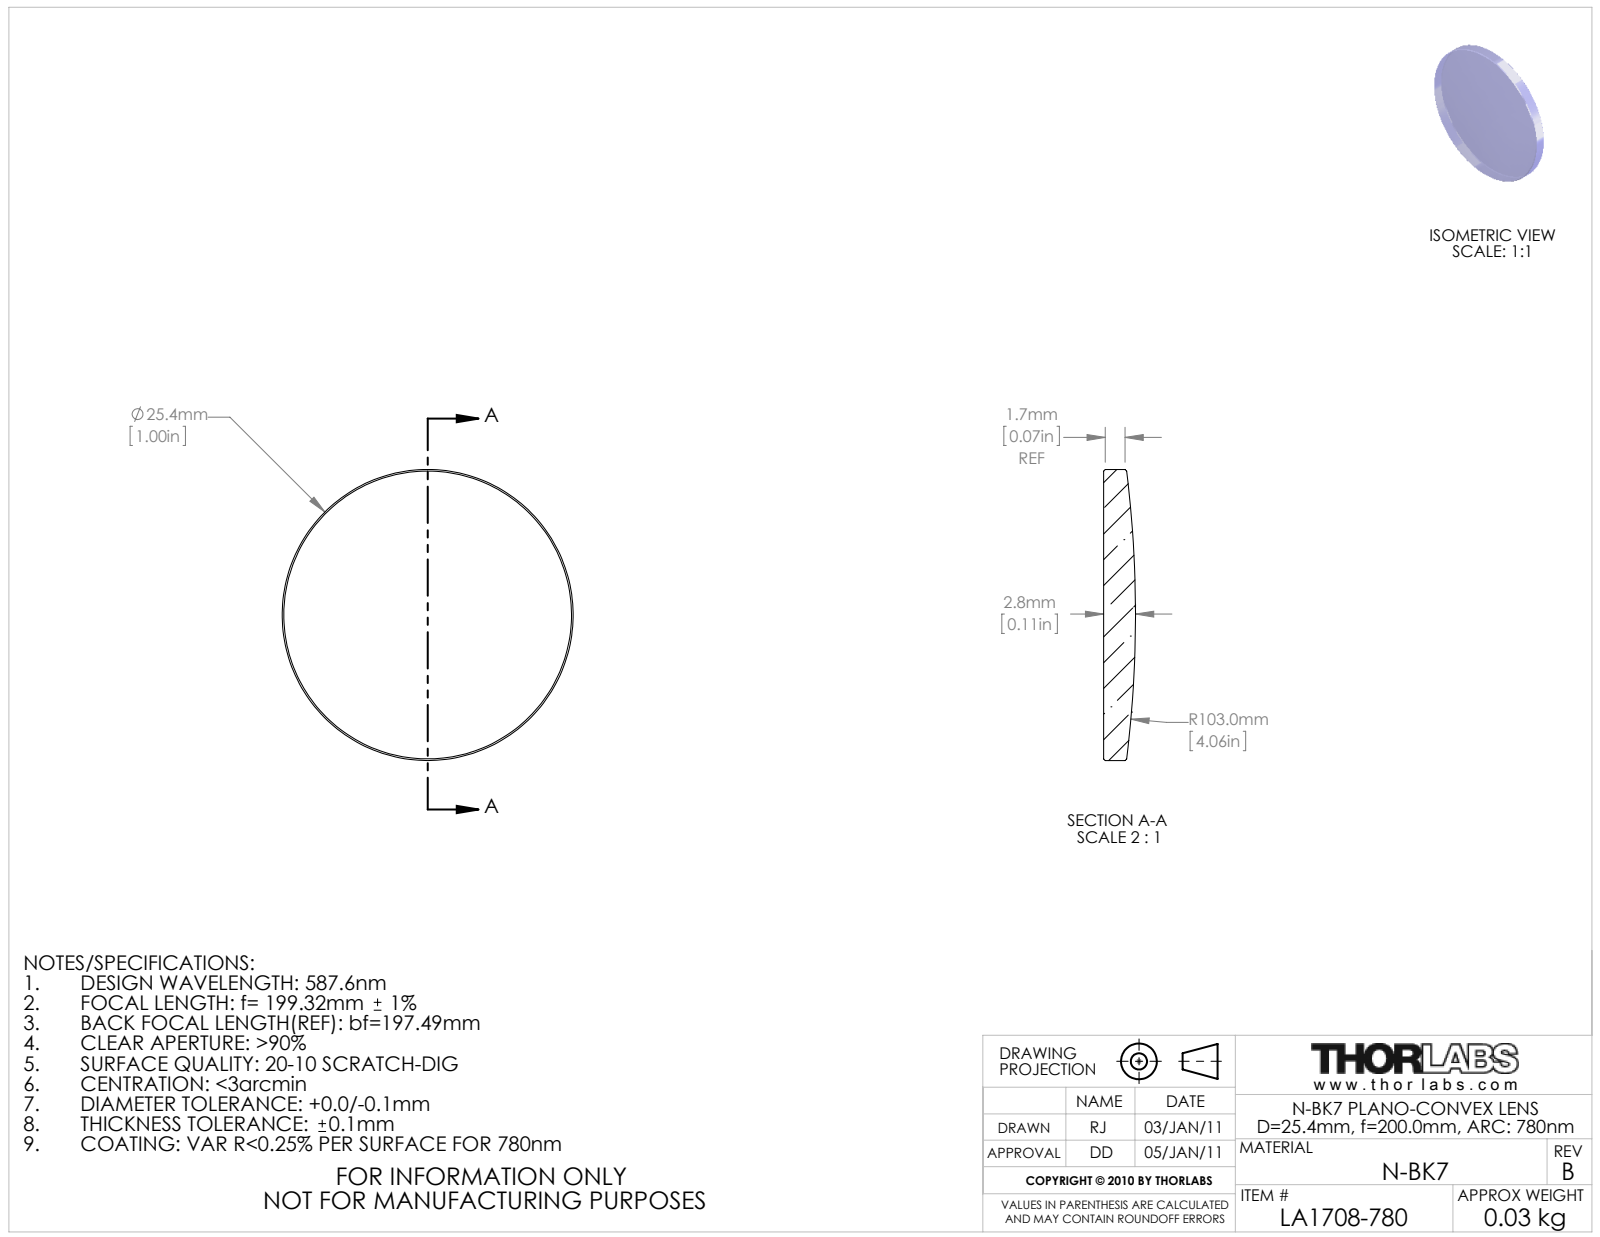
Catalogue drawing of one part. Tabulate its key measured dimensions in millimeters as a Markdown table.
| quantity | value |
| --- | --- |
| part name | 21799-E0W |
| STEP written by | SolidWorks 2011 (AUTOMOTIVE_DESIGN) |
| units | millimeters |
| bodies | 0 solids, 9 faces (1 planar, 2 cylindrical, 6 other) |
| overall size | 25.4 × 25.4 × 2.78 |
| round bosses / shafts (diameter × count) | 25.4 × 1 |
